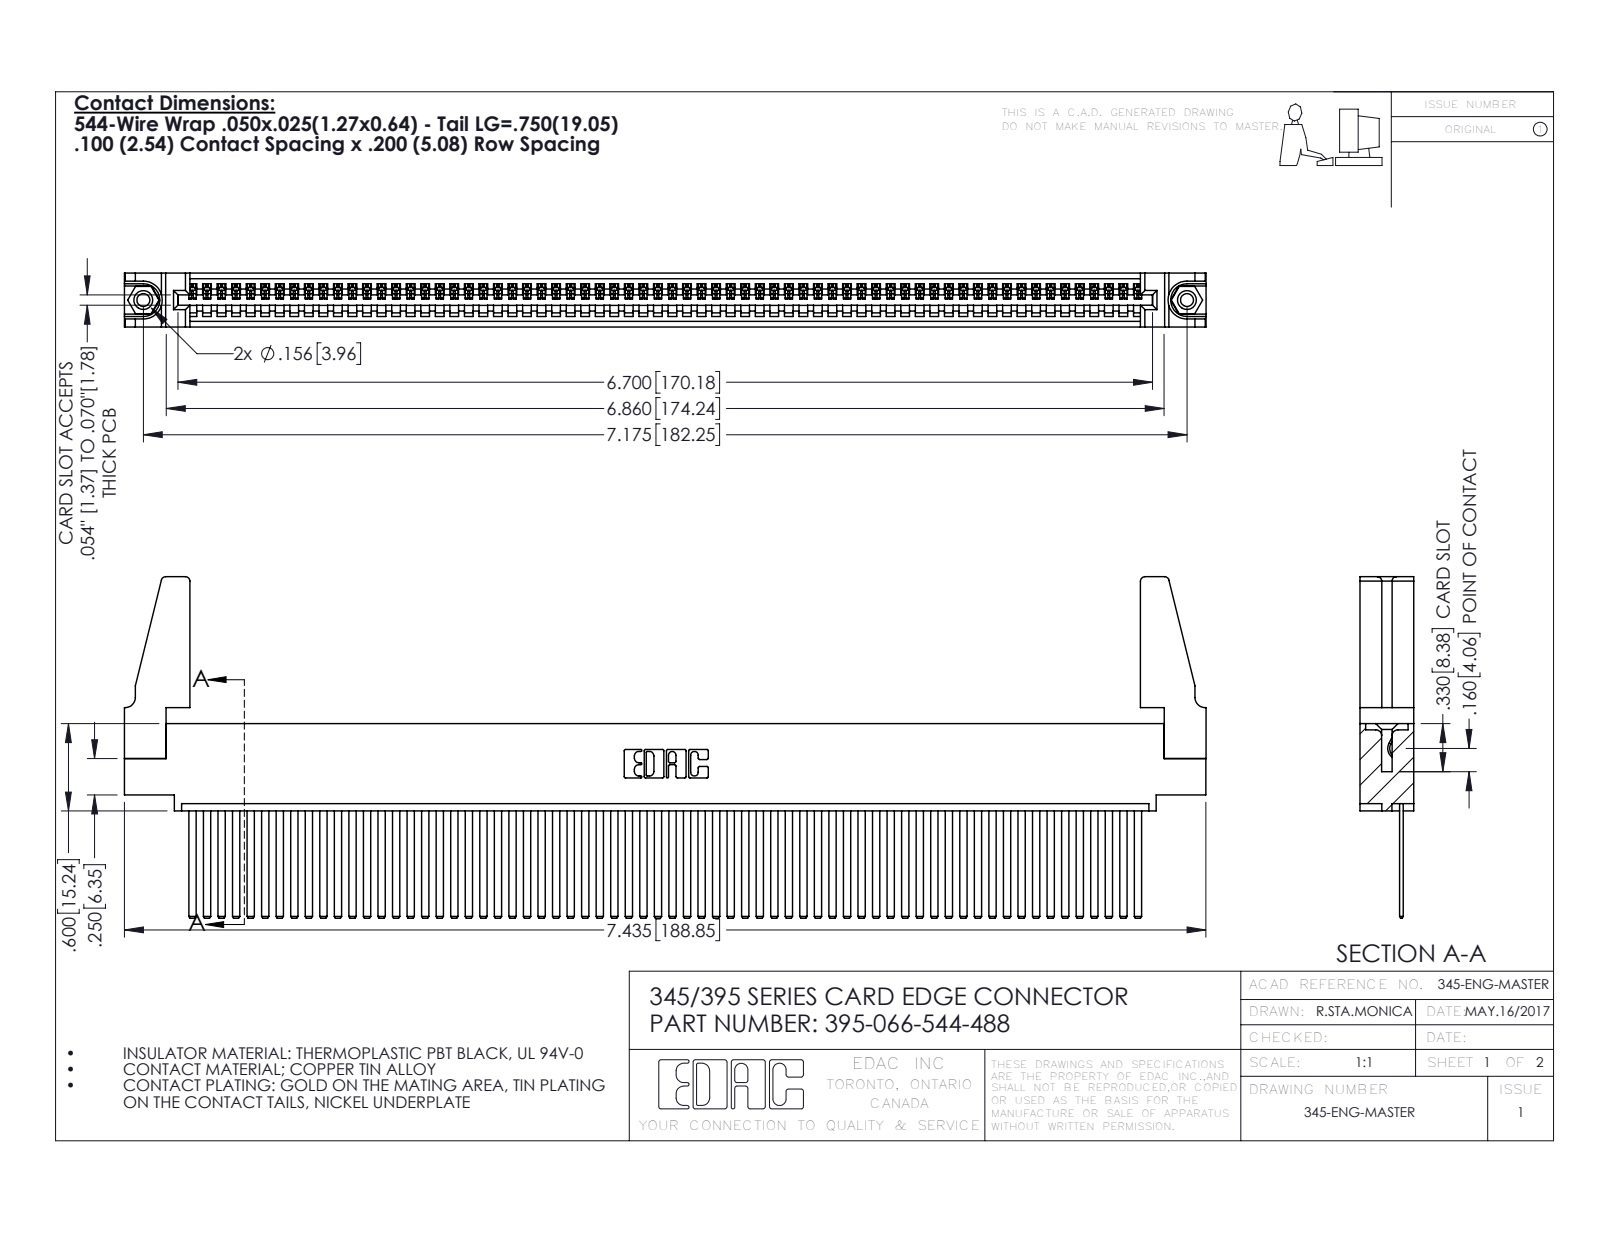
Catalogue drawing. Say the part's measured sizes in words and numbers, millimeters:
The part is named "345 Part_0.110 Offset - 0.156 Dia-TH; 345-220-078_345-220-088; 345-292-001_345-293-144; 345-250-001_345-250-001-102 (+1 more)". Its 3-D file was written by "SolidWorks 2016 (CONFIG_CONTROL_DESIGN)". It is 71 solids with 3686 faces: 2532 planar, 1138 cylindrical and 16 other. Overall it measures 188.9 by 59.6 by 9.4 millimeters. Its volume is 22 070 cubic millimeters and its surface area 30 850 square millimeters. Round holes: 2 of diameter 2.3, 2 of diameter 3.2, 2 of diameter 4, 1 of diameter 1.6. Round bosses or shafts: 2 of diameter 3.9. Partial cylindrical surfaces (rounded edges, fillets, slot ends): 132 of radius 0.2, 22 of radius 0.3, 8 of radius 0.8, 6 of radius 0.2, 6 of radius 0.8, 3 of radius 0.7, 2 of radius 0.8, 2 of radius 1. The main face-to-face distances are 1.8, 7.6, 2.5, 6.9, 0.6, 9.4, 5.1, 5.7, 3.8, 1.8. The hole center spacings are 6.9, 176.3, 182.2.
